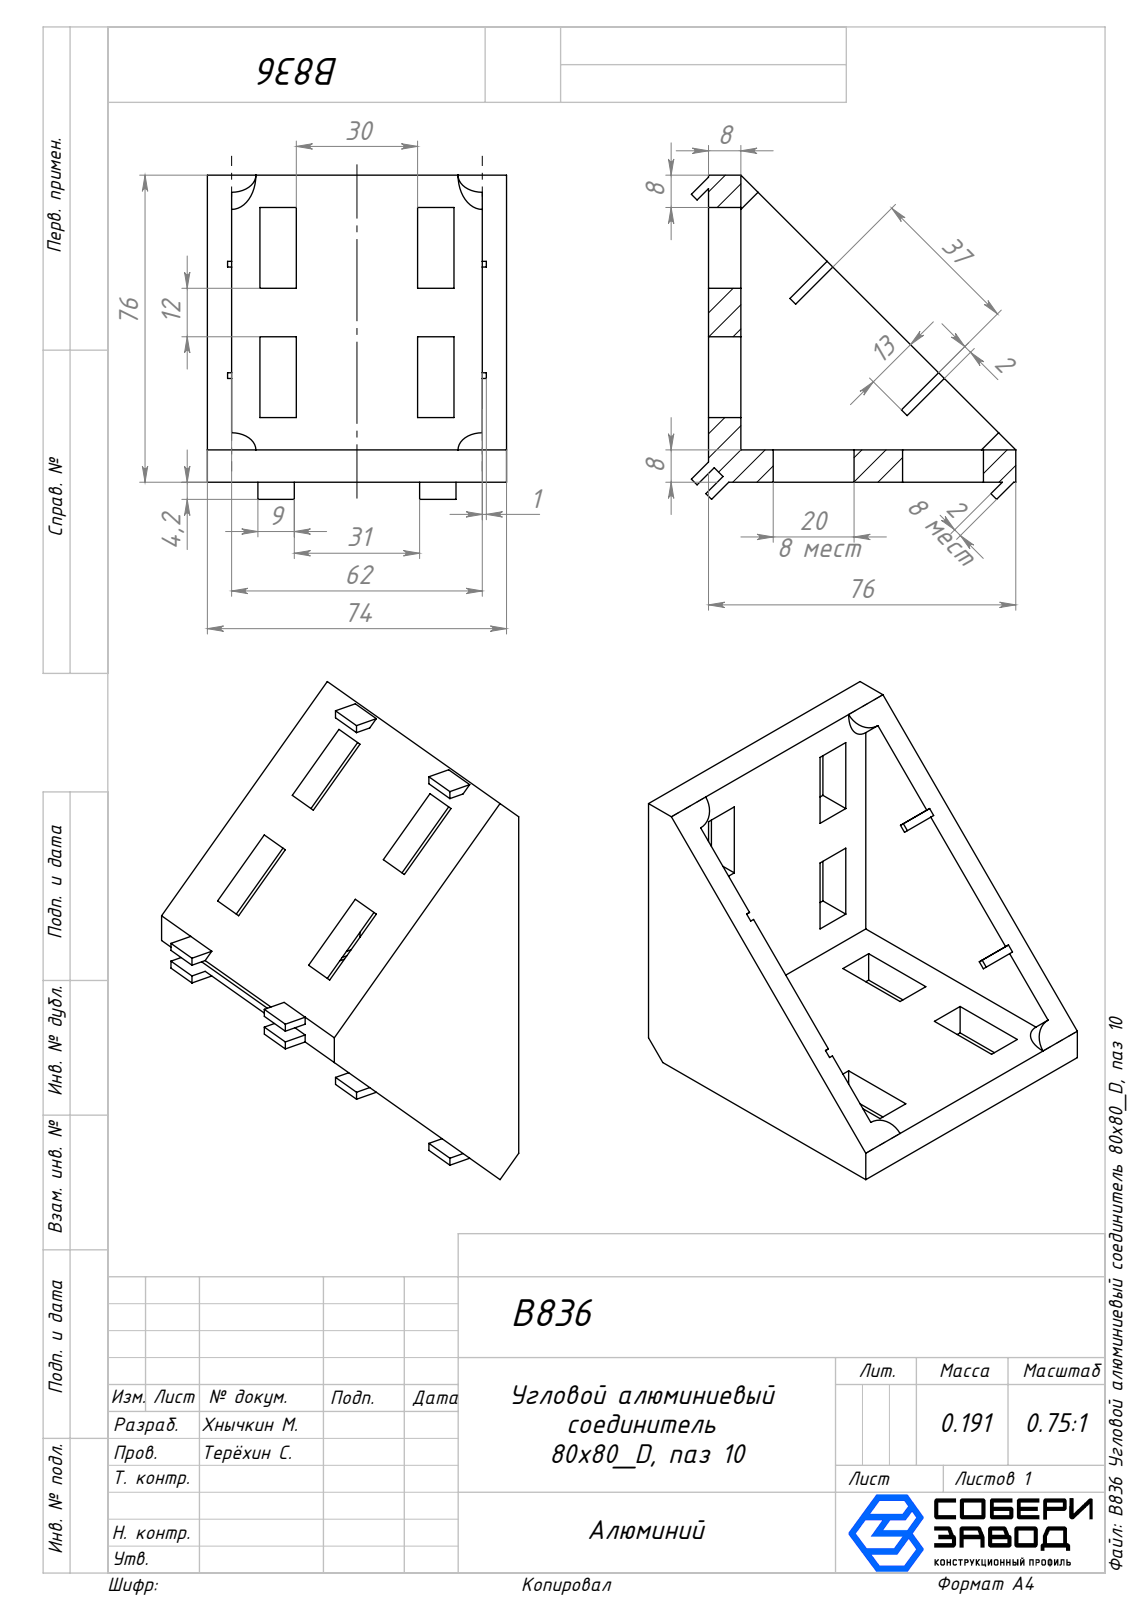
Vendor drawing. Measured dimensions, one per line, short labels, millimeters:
name: B836 Угловой алюминиевый соединитель 80х80_D, паз 10
written by: SolidWorks 2025 (AUTOMOTIVE_DESIGN)
unit: mm
bodies: 1 solid, 103 faces (99 planar, 4 cylindrical, 0 other)
size: 80.24 × 80.24 × 74
volume: 101 647 mm³; area: 35 395 mm²
rounds: 4× R6
face distances: 8, 68, 6, 74, 62, 52, 16, 9, 13, 22
